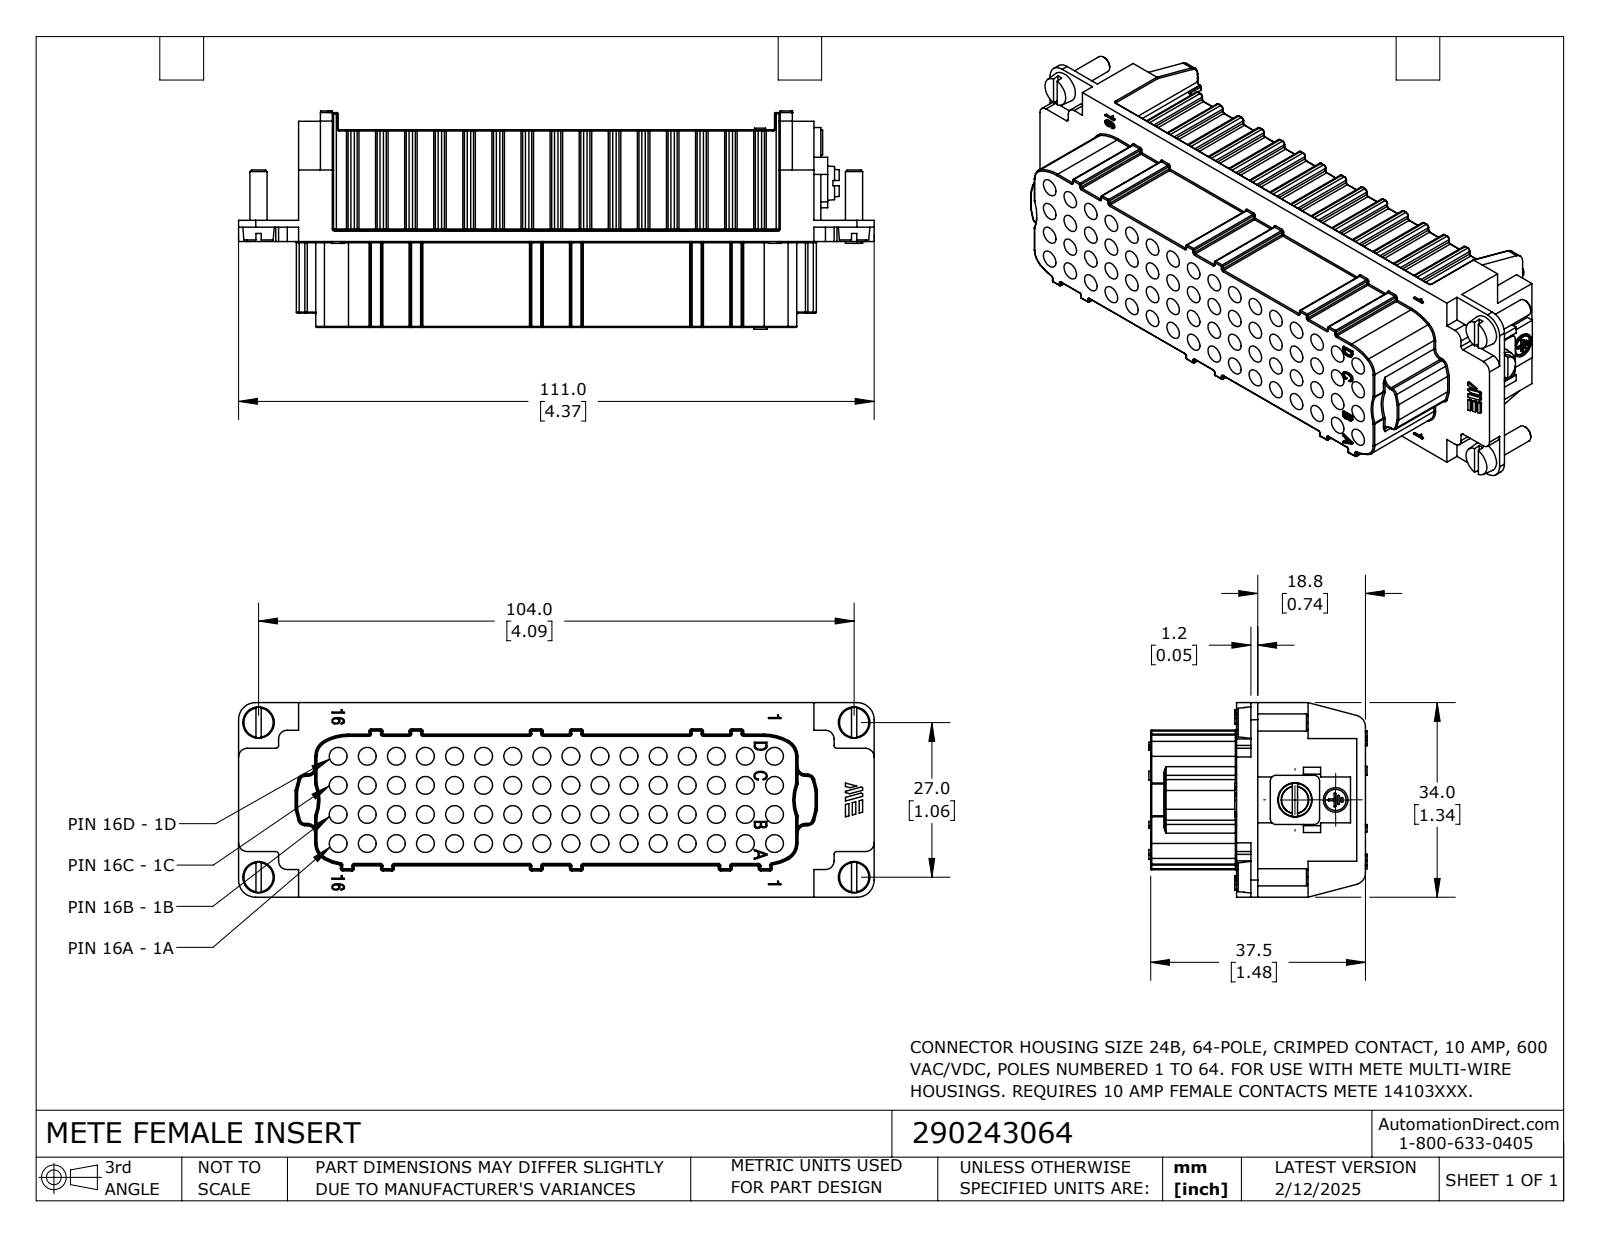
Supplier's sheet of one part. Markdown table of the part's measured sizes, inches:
| quantity | value |
| --- | --- |
| part name | 290243064 |
| STEP written by | SolidWorks 2024 (CONFIG_CONTROL_DESIGN) |
| units | inches |
| bodies | 1 solid, 1812 faces (470 planar, 803 cylindrical, 539 other) |
| overall size | 4.37 × 1.5 × 1.339 |
| volume | 3.577 in³ |
| surface area | 60.33 in² |
| round holes (diameter × count) | 0.122 × 64, 0.146 × 1 |
| round bosses / shafts (diameter × count) | 0.118 × 4, 0.169 × 1 |
| partial cylindrical surfaces (radius × count) | 0.008 × 210, 0.02 × 72, 0.012 × 60, 0.004 × 14, 0.059 × 12, 0.039 × 8, 0.085 × 8, 0.118 × 8 |
| main face-to-face distances | 0.024, 0.866, 0.591, 0.768, 1.358, 0.669, 0.689, 0.079, 0.89, 0.843 |
| hole center spacings | 0.632, 0.447, 0.4, 0.283, 1.02, 0.2, 0.566, 0.721 |
